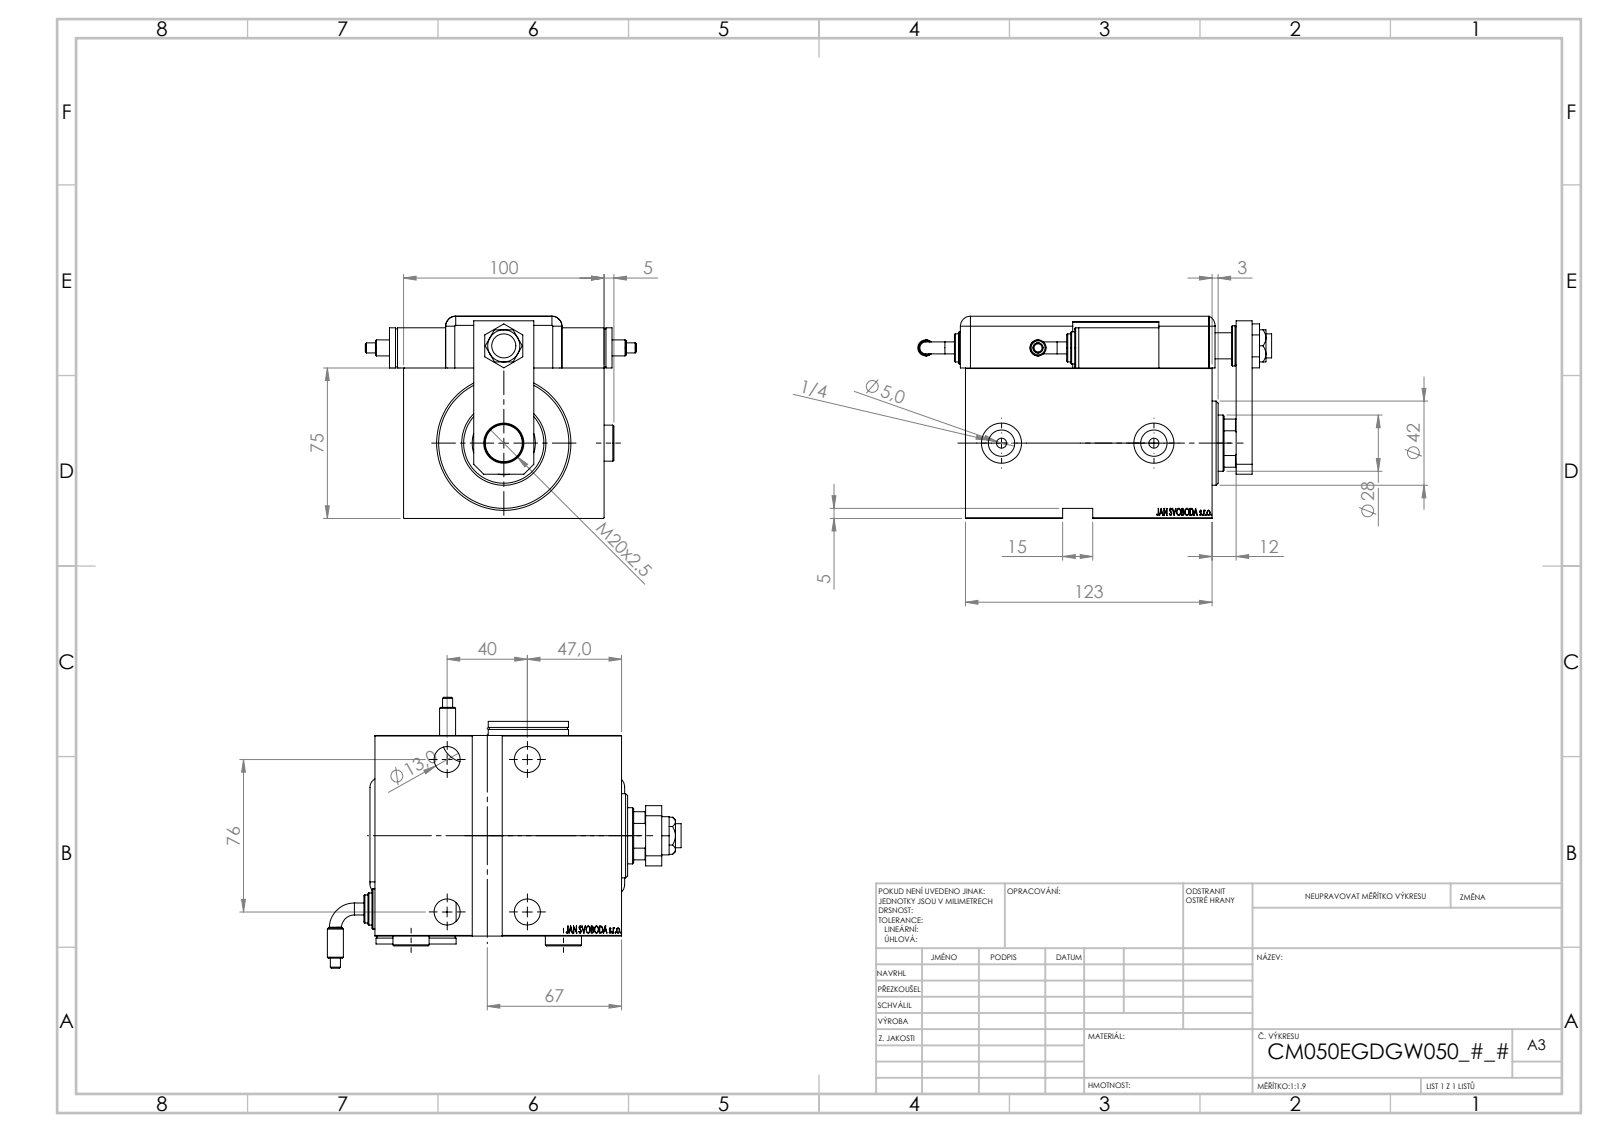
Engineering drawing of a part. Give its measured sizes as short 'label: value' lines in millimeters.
name: MAGNETIC SWITCH Q; NUT_D19; SWITCH_Q_FRONT_BACK; TYC (+7 more)
written by: SolidWorks 2019 (CONFIG_CONTROL_DESIGN)
unit: mm
bodies: 15 solids, 1324 faces (656 planar, 131 cylindrical, 537 other)
size: 176.46 × 135.01 × 100.8
volume: 953 320 mm³; area: 184 466 mm²
holes: 5× ⌀13, 4× ⌀19, 3× ⌀20, 2× ⌀4, 2× ⌀5, 2× ⌀8, 2× ⌀13.16, 1× ⌀12, 1× ⌀14, 1× ⌀18.5, 1× ⌀28, 1× ⌀31.5
bosses: 3× ⌀20, 2× ⌀18, 2× ⌀16, 2× ⌀14, 2× ⌀8, 2× ⌀6, 2× ⌀5.04, 1× ⌀52
rounds: 9× R5, 1× R10, 1× R13.5
face distances: 3, 75, 100, 123, 100.8, 25.8, 14, 20, 109, 5
hole spacings: 76, 40, 47.2, 61.22, 82.87, 85.88, 91.59, 20
